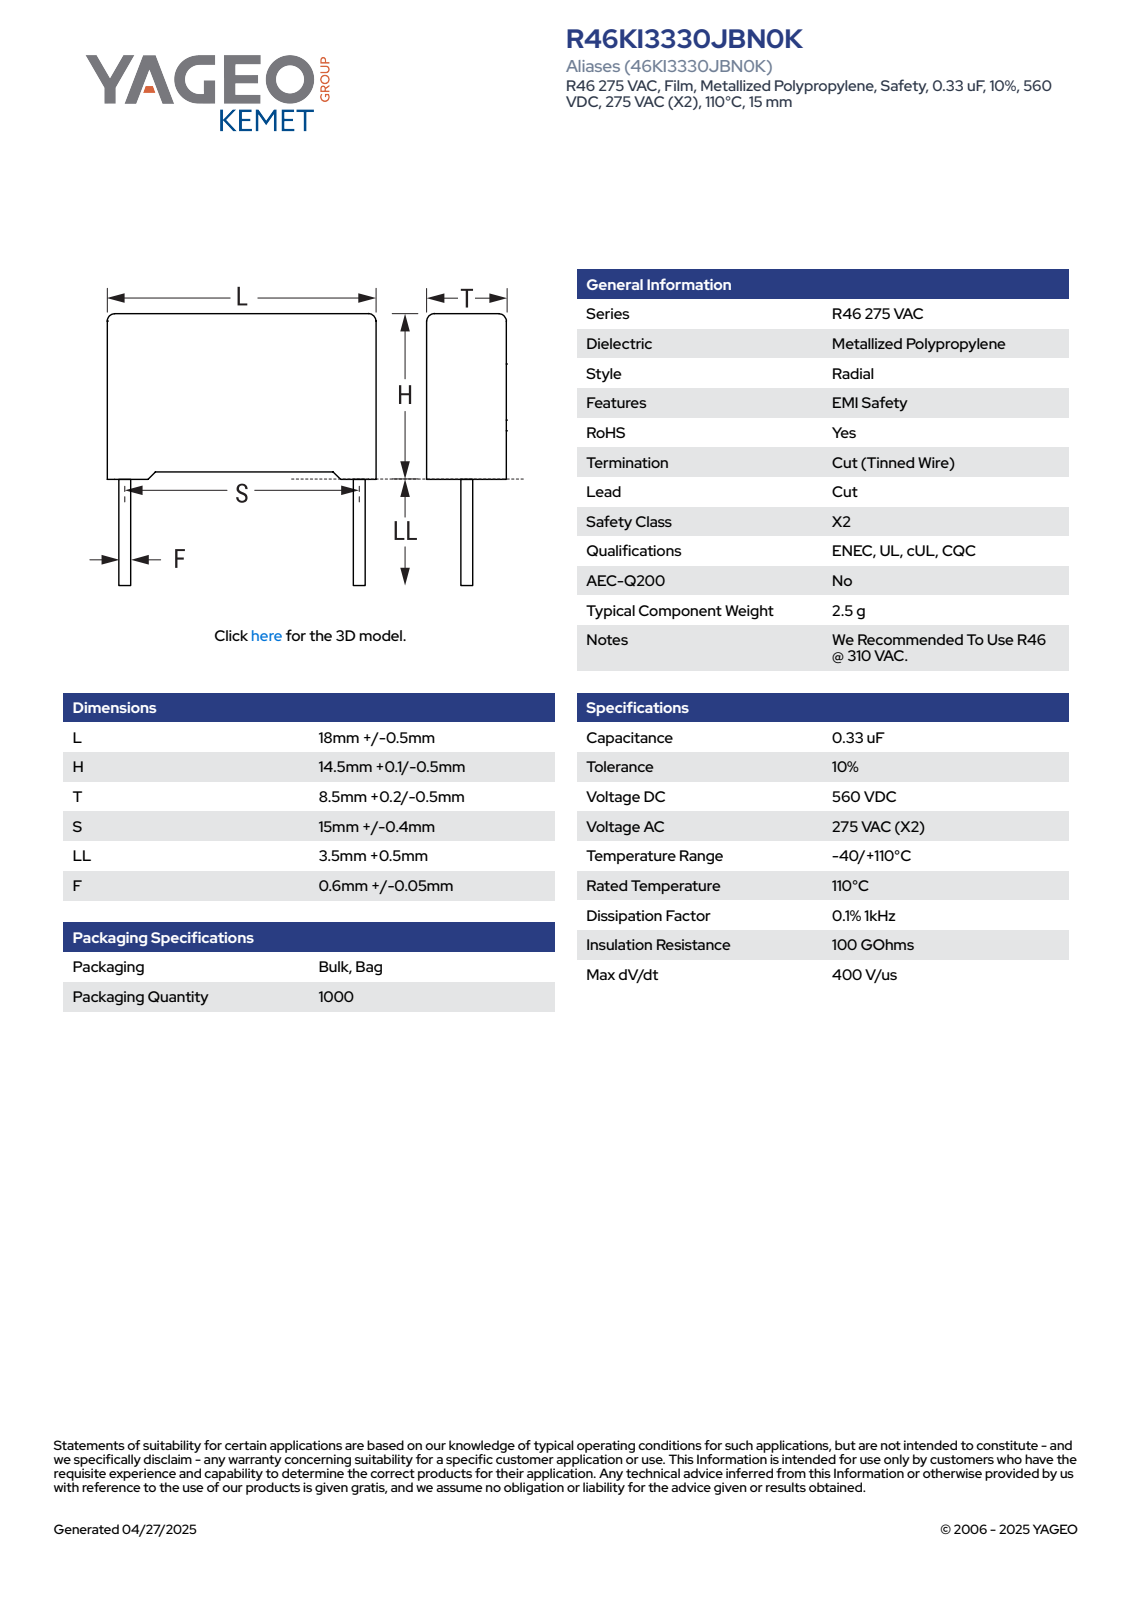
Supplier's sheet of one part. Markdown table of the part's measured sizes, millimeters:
| quantity | value |
| --- | --- |
| part name | CFR_RB2_18X14.5X8.5_L18.5H14.6T8.7S15LL4F0.65 |
| STEP written by | SolidWorks 2021 (AUTOMOTIVE_DESIGN) |
| units | millimeters |
| bodies | 4 solids, 85 faces (77 planar, 8 cylindrical, 0 other) |
| overall size | 18.6 × 18.5 × 8.71 |
| volume | 2 246 mm³ |
| surface area | 1 164 mm² |
| round bosses / shafts (diameter × count) | 0.65 × 2 |
| partial cylindrical surfaces (radius × count) | 0.5 × 4 |
| main face-to-face distances | 8.7, 13.85, 18.5, 0.62, 0.75, 14.6, 8.08, 0.5, 14.1, 17.88 |
